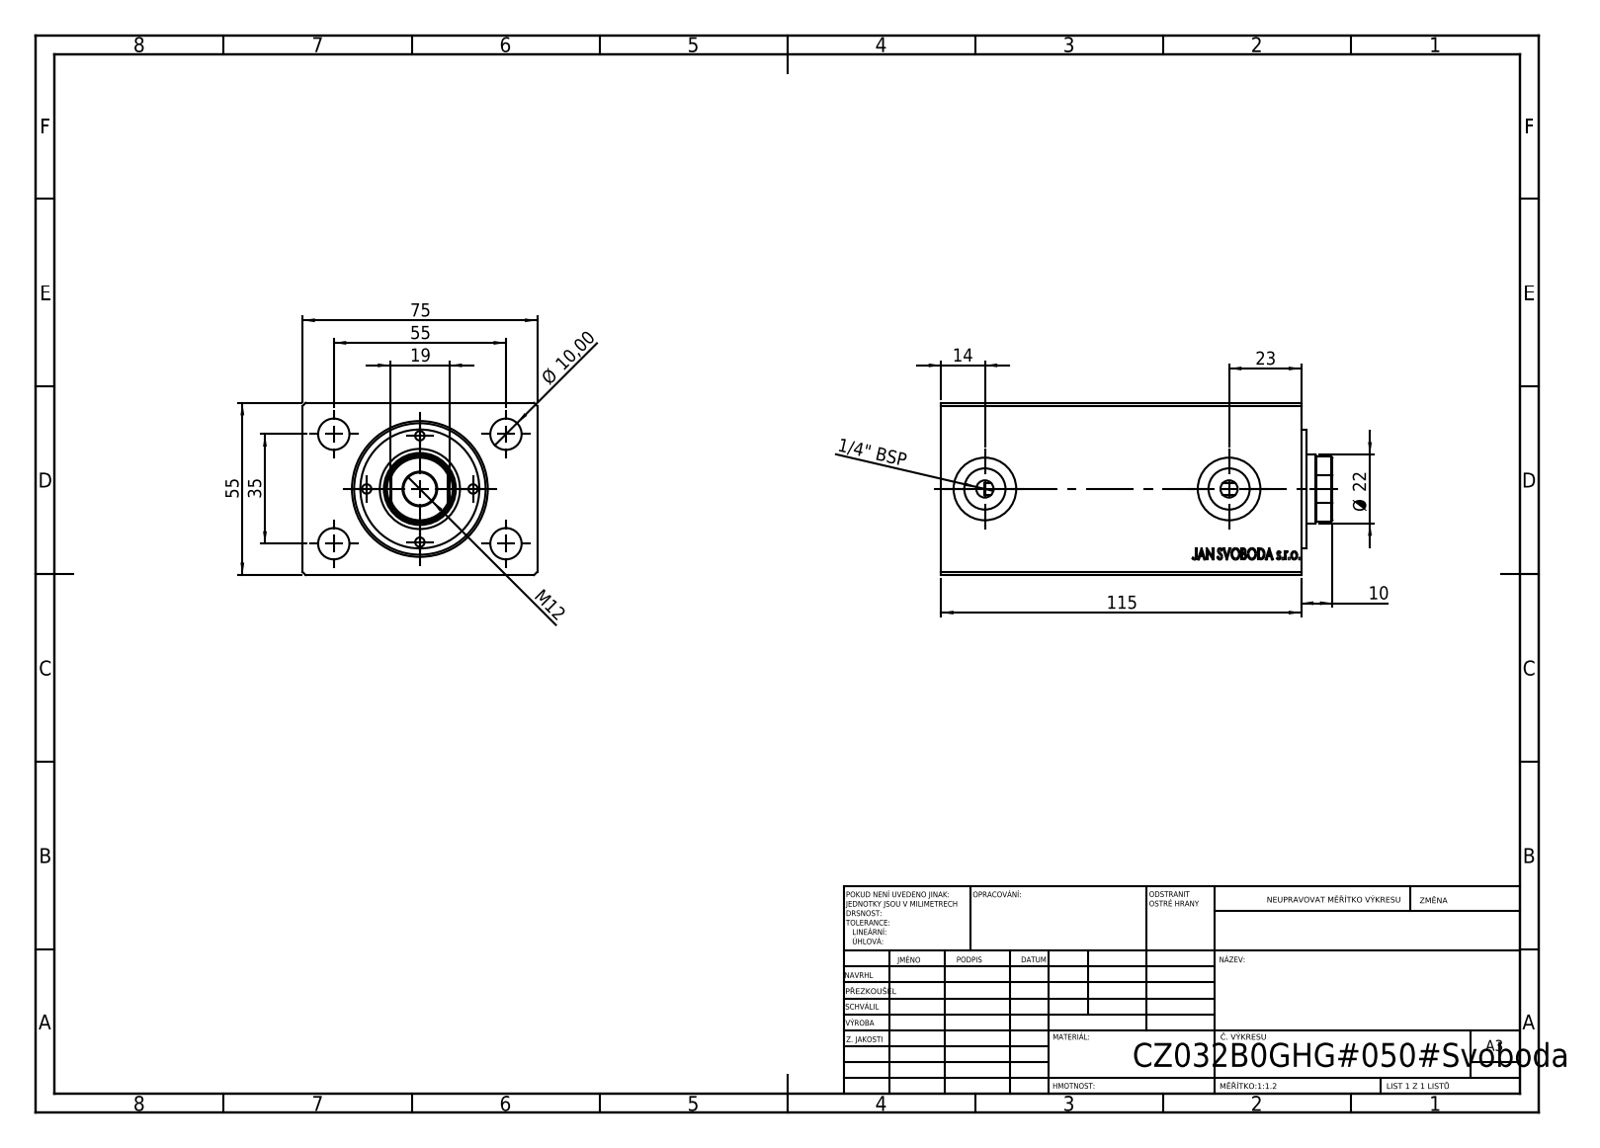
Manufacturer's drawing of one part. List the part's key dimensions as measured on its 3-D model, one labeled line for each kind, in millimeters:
Part name (STEP PRODUCT): V500CZ; V500CZ_B_VC
STEP written by: SolidWorks 2019 (CONFIG_CONTROL_DESIGN)
Units: millimetres
Bodies: 3 solids, 875 faces (401 planar, 58 cylindrical, 416 other)
Overall size (bounding box): 125 × 75 × 55
Volume: 433 980 mm³ · Surface area: 71 183 mm²
Round holes (diameter × count): ⌀3 ×4, ⌀10 ×4, ⌀5.5 ×2, ⌀13.16 ×2, ⌀20 ×2, ⌀10.5 ×1, ⌀22 ×1, ⌀23 ×1, ⌀32 ×1, ⌀36 ×1, ⌀42 ×1
Round bosses / shafts (diameter × count): ⌀38 ×1
Partial cylindrical surfaces — rounded edges, fillets, slot ends (radius × count): R10.5 ×1
Main face-to-face distances: 55, 75, 115, 101.2, 13.8, 10, 13.6, 8.2, 1.8, 114.8
Hole centre spacings: 17, 20.41, 24.04, 27.5, 32.6, 44.12, 47.82, 34
